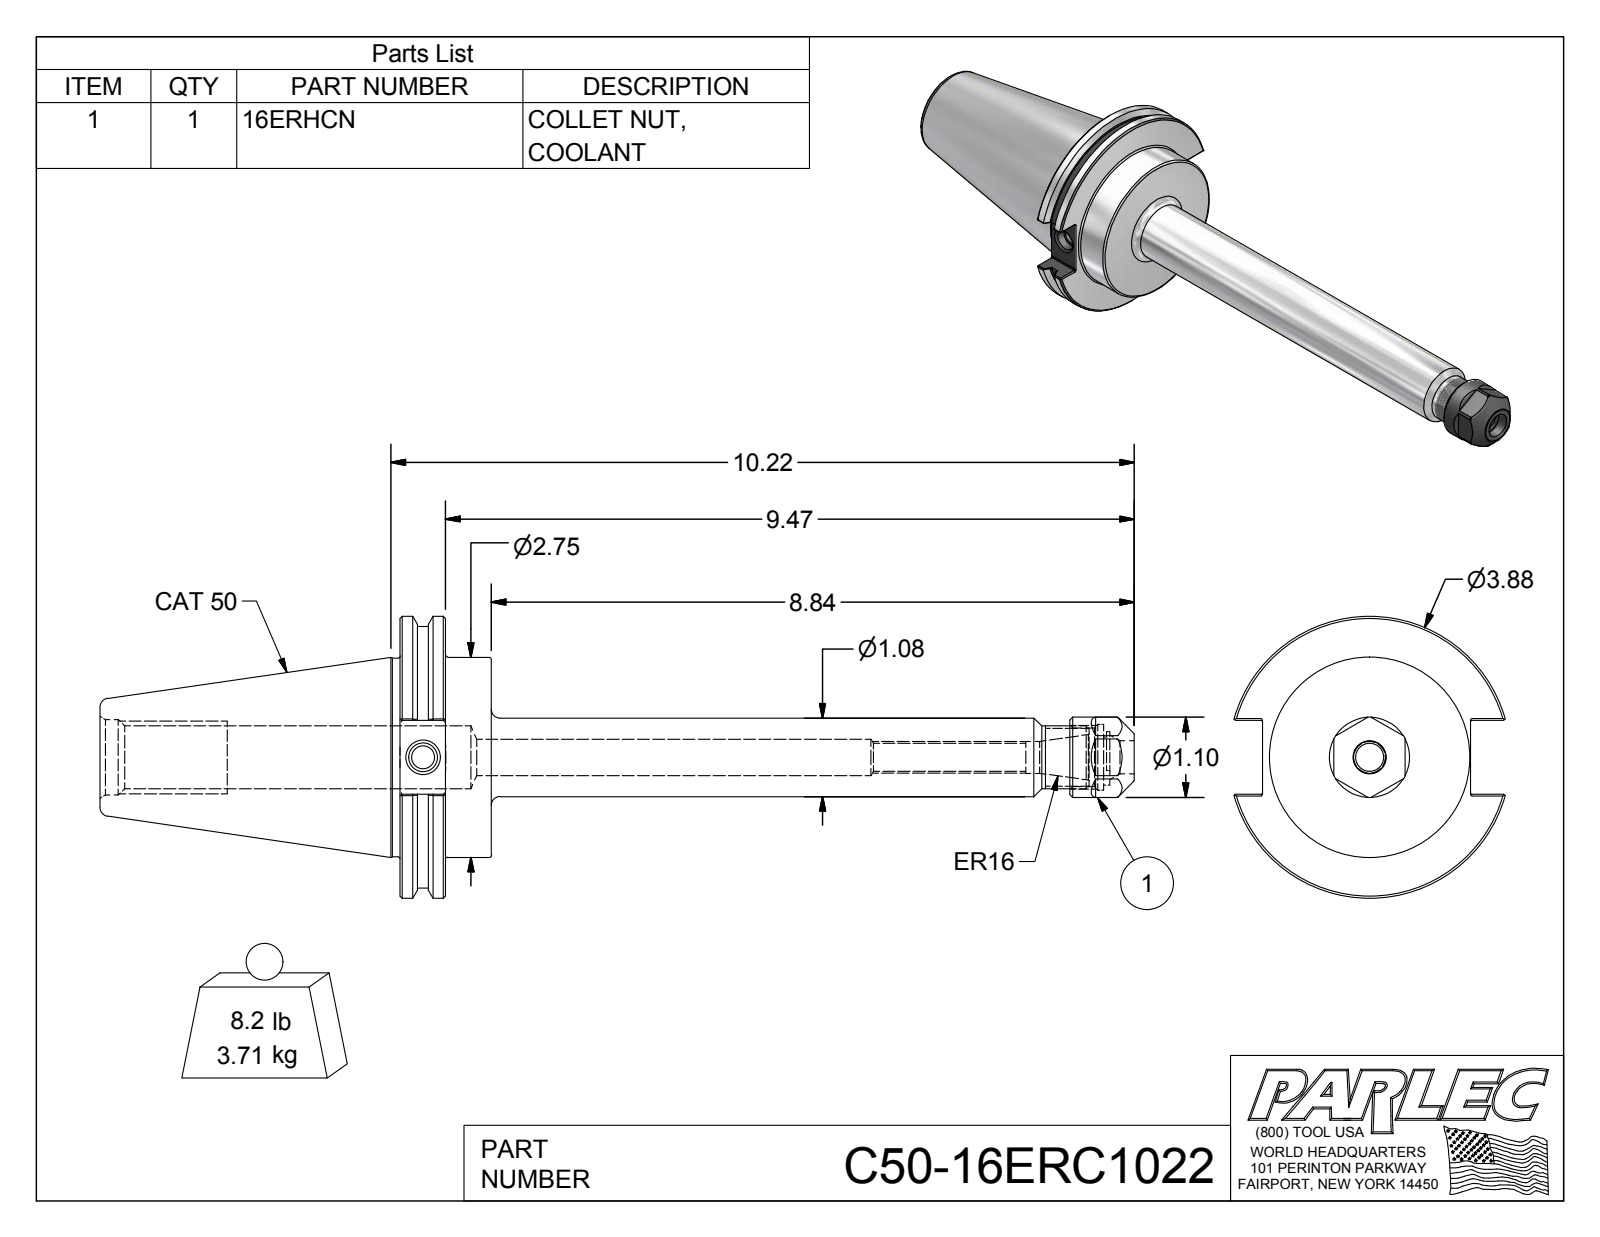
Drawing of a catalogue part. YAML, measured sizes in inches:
part_name: "C50-16ERC1022; C50-16ER10-1; 16ERHCN"
step_written_by: "Autodesk Inventor 2012 (AUTOMOTIVE_DESIGN)"
units: inches
bodies: {solids: 2, faces: 130, planar: 50, cylindrical: 35, other: 45}
overall_size: [14.22, 3.875, 3.729]
volume: 29.06
surface_area: 120.5
round_holes:
  - {diameter: 0.315, count: 1}
  - {diameter: 0.383, count: 1}
  - {diameter: 0.399, count: 1}
  - {diameter: 0.44, count: 1}
  - {diameter: 0.453, count: 1}
  - {diameter: 0.5, count: 1}
  - {diameter: 0.661, count: 1}
  - {diameter: 0.807, count: 1}
  - {diameter: 0.865, count: 1}
  - {diameter: 0.906, count: 1}
  - {diameter: 1.038, count: 1}
round_bosses_or_shafts:
  - {diameter: 3.875, count: 1}
  - {diameter: 3.594, count: 1}
  - {diameter: 2.75, count: 1}
  - {diameter: 2.73, count: 1}
  - {diameter: 1.102, count: 1}
  - {diameter: 1.08, count: 1}
  - {diameter: 0.866, count: 1}
partial_cylinders:
  - {radius: 0.02, count: 12}
  - {radius: 0.354, count: 1}
face_to_face_distances: [1.255, 0.625, 0.63, 0.979, 4.125, 4.75, 5.38, 2.86, 1.015, 0.866]
hole_center_spacings: [0.051]
